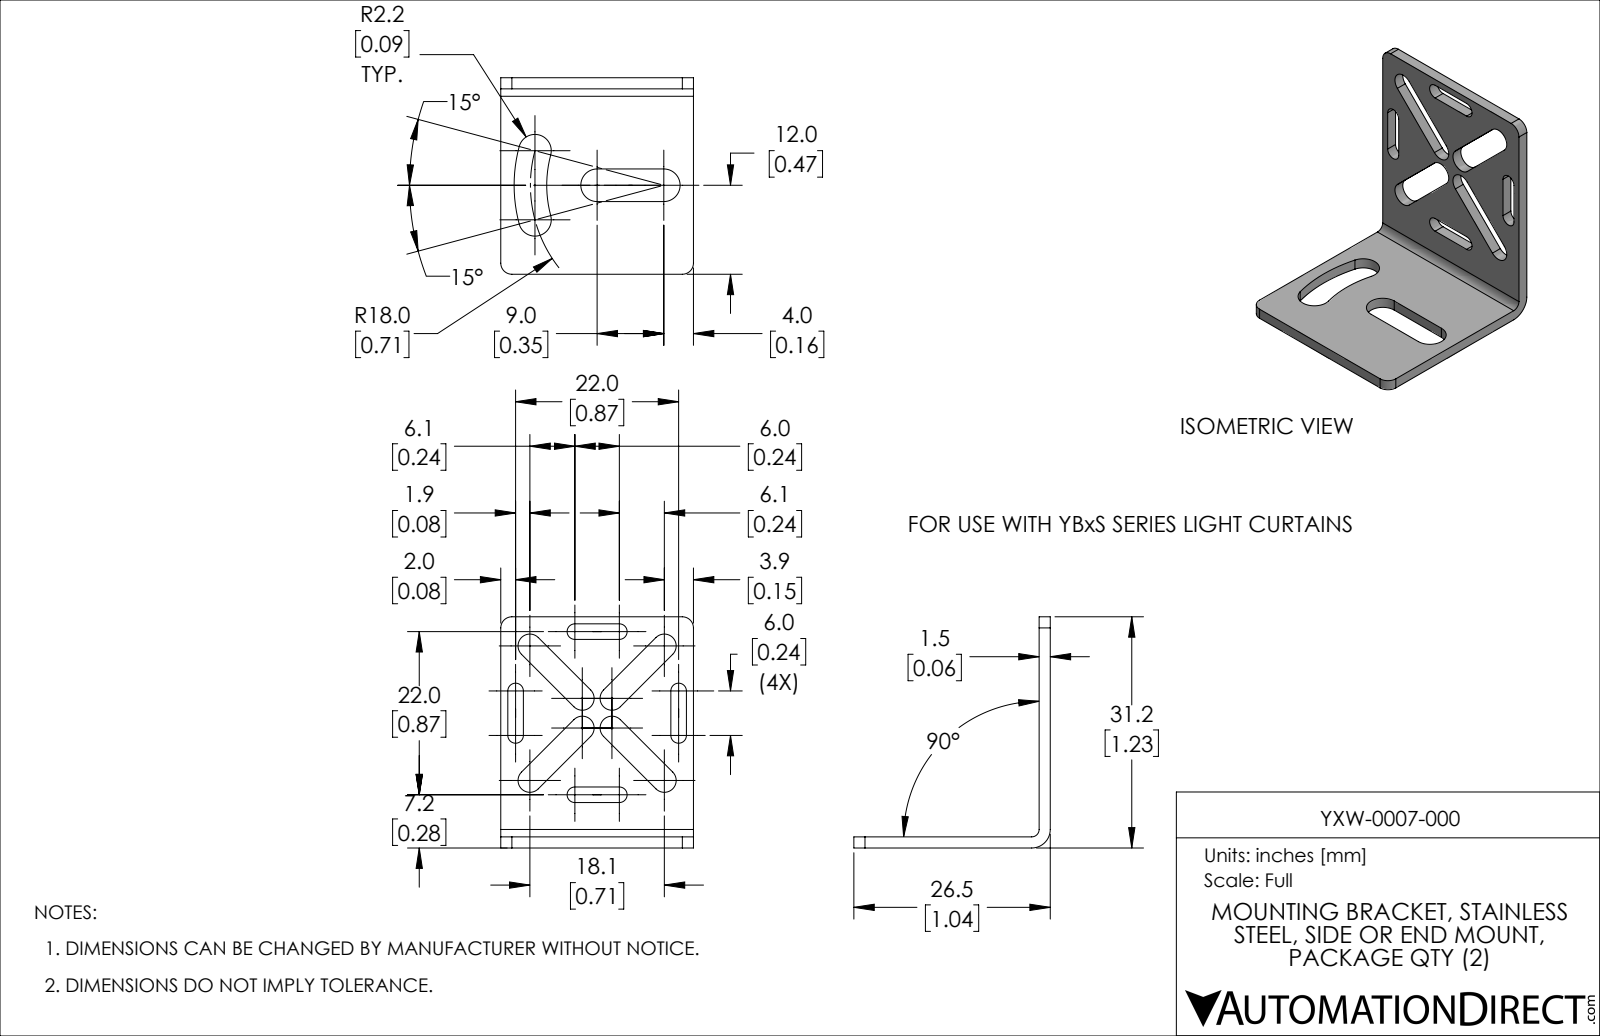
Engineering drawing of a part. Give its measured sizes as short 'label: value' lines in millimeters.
name: YXW-0007-000
written by: PARTsolutions (CONFIG_CONTROL_DESIGN)
unit: mm
bodies: 1 solid, 54 faces (26 planar, 28 cylindrical, 0 other)
size: 31.18 × 26.5 × 26
volume: 1 655 mm³; area: 2 836 mm²
rounds: 8× R1.05, 8× R1.6, 4× R1.5, 4× R2.2, 1× R1, 1× R2.5, 1× R15.8, 1× R20.2
face distances: 1.5, 26, 3.2, 2.1, 22, 31.18, 29.68, 26.5, 25, 25.05
